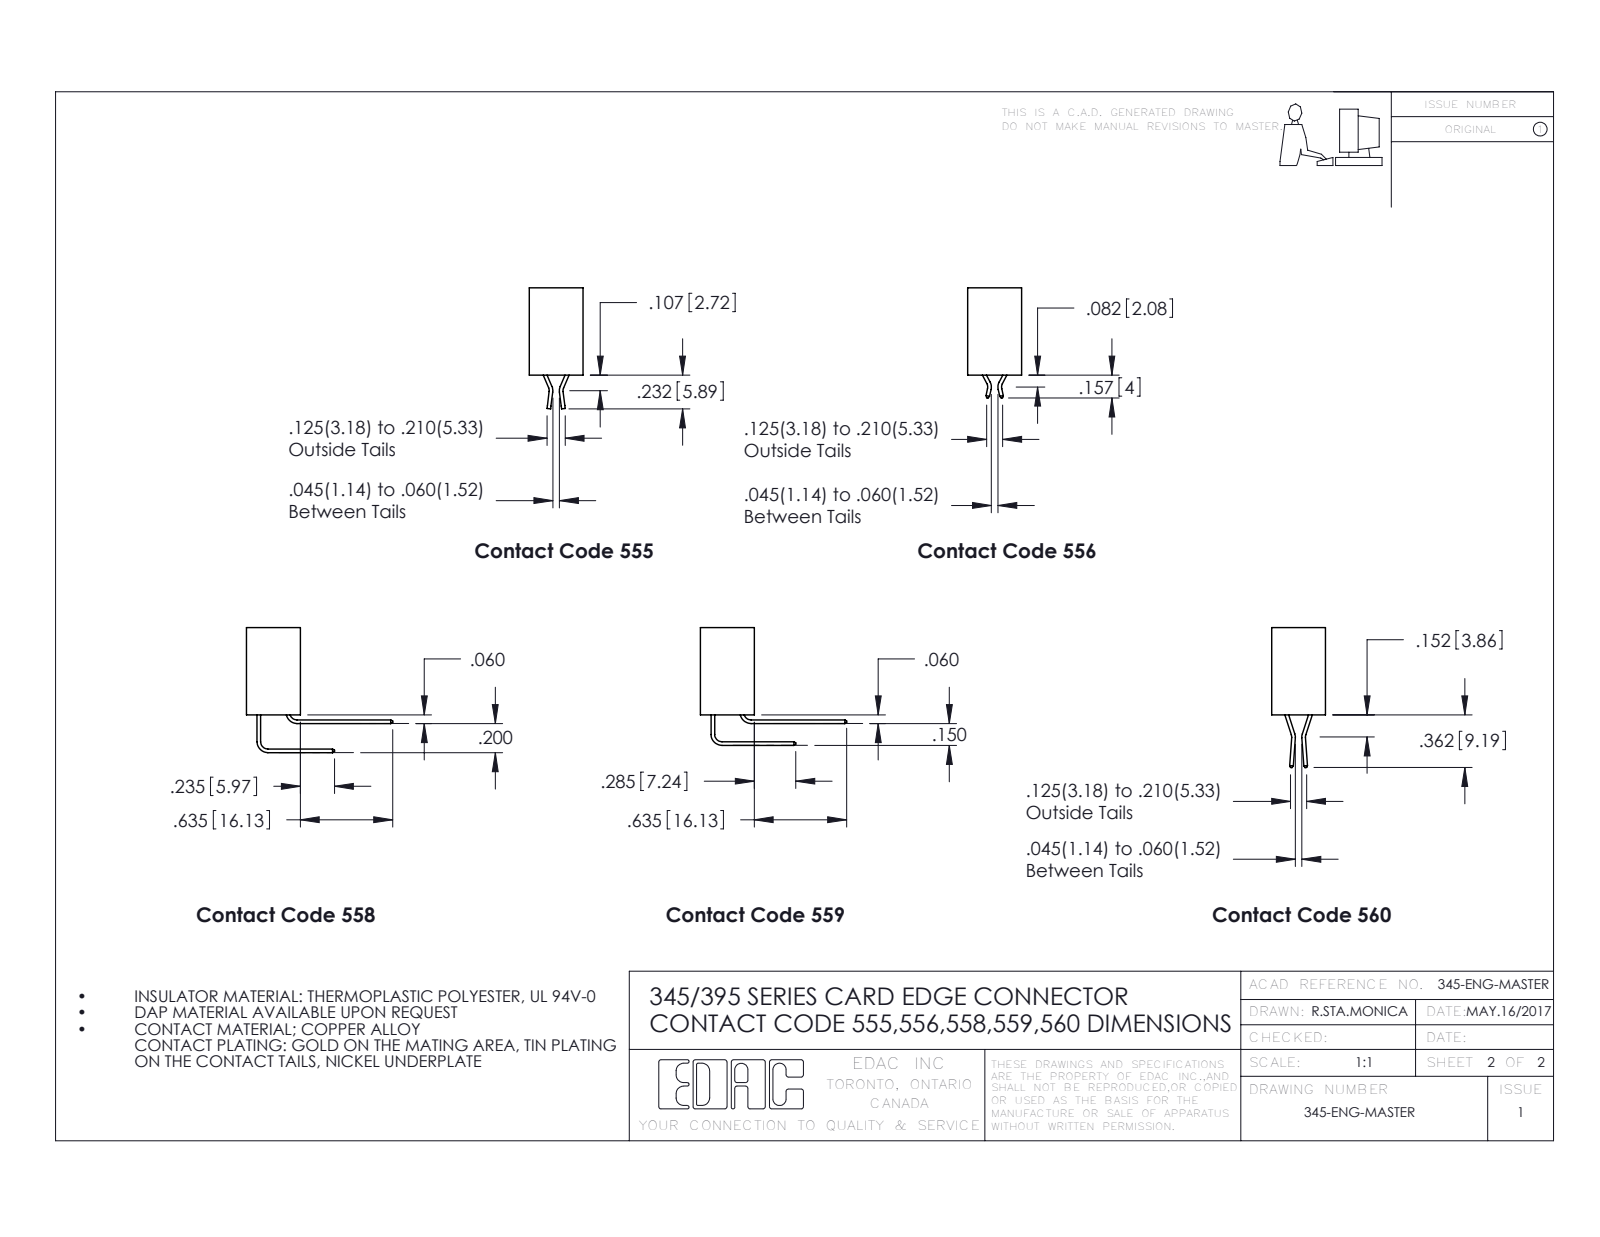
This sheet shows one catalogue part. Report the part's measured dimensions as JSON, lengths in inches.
{"part_name": "345-292-001_345-293-125; 345 Part_Flush Mounting Lugs - Side Mount; 345-005-525-112", "step_written_by": "SolidWorks 2020 (CONFIG_CONTROL_DESIGN)", "units": "inches", "bodies": {"solids": 6, "faces": 436, "planar": 310, "cylindrical": 126, "other": 0}, "overall_size": [1.335, 0.737, 0.37], "volume_in3": 0.171, "surface_area_in2": 4.683, "round_holes": [[0.128, 2], [0.064, 1]], "partial_cylinders_radius": [[0.01, 22], [0.006, 10], [0.007, 6], [0.031, 6], [0.026, 3], [0.031, 2], [0.04, 2], [0.014, 1]], "face_to_face_distances": [0.2, 0.37, 0.1, 0.298, 0.072, 0.25, 0.06, 0.025, 0.55, 0.35], "hole_center_spacings": [1.075]}
